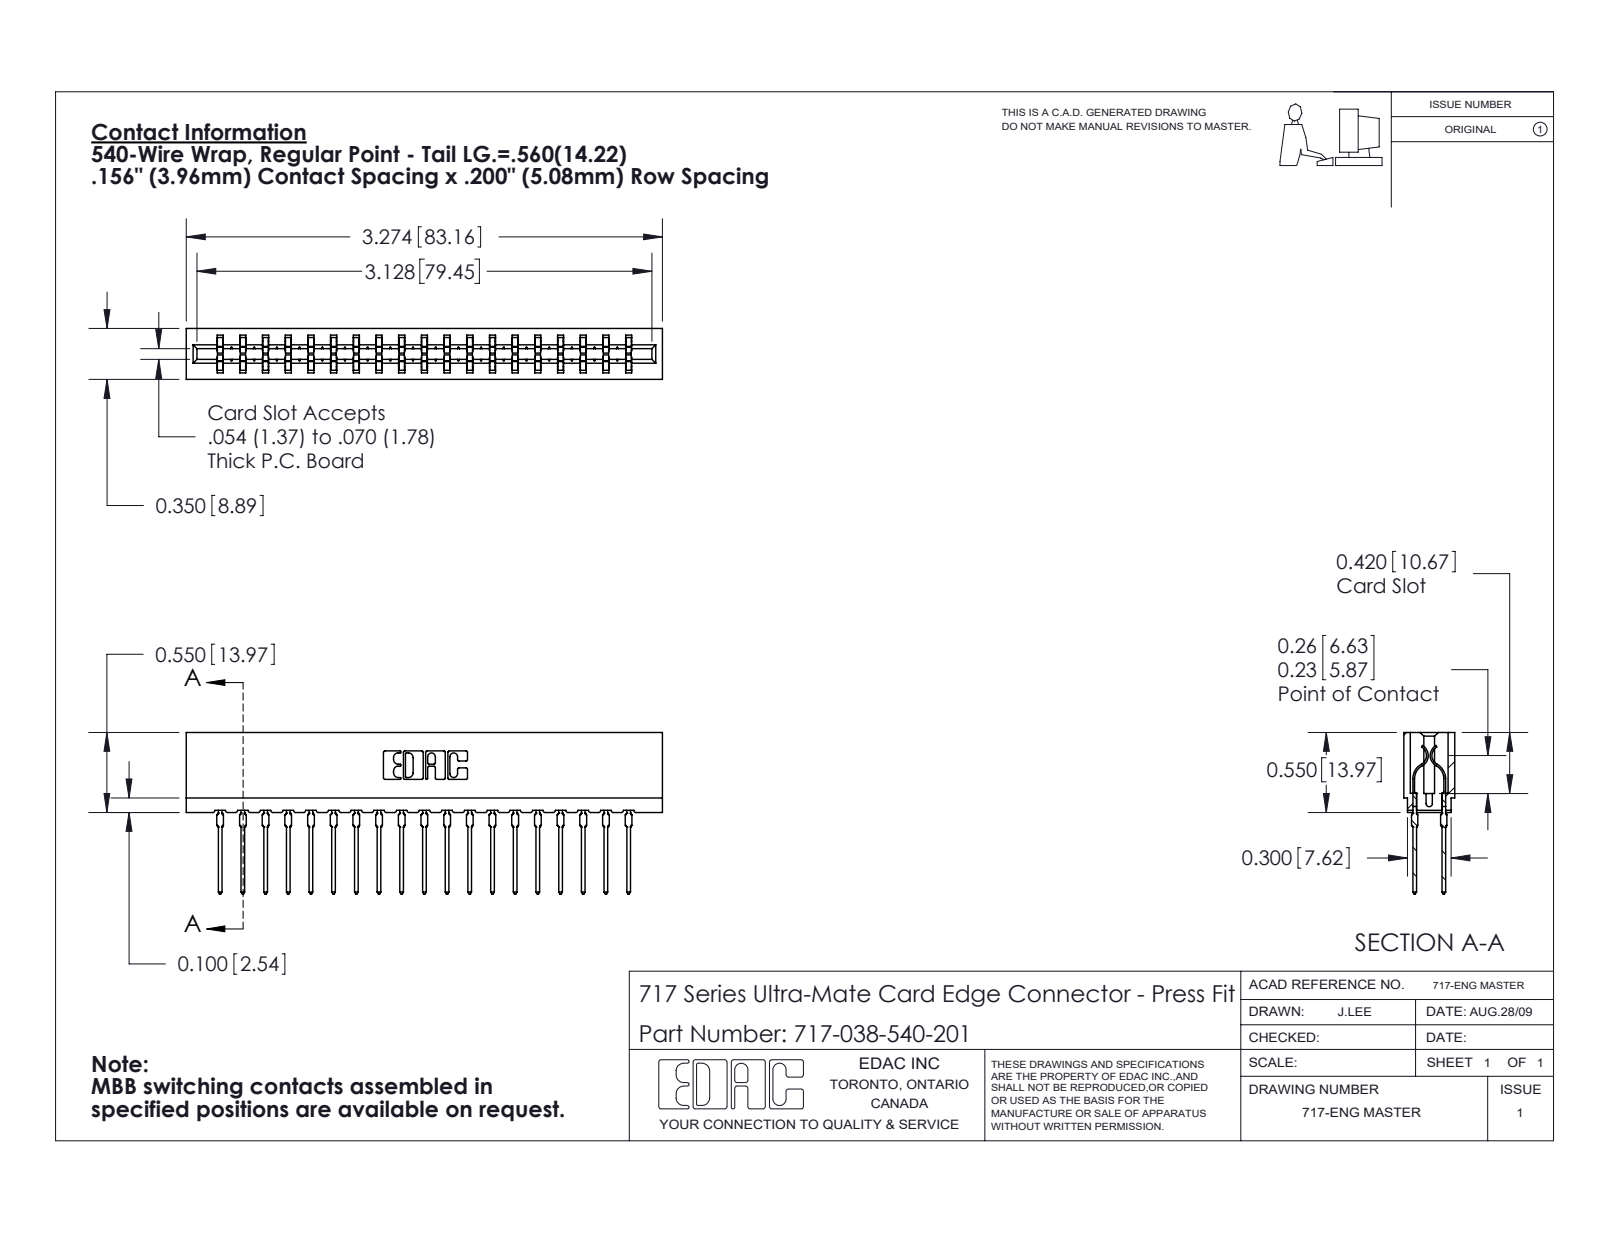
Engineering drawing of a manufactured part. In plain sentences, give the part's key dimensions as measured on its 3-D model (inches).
The part is named "717-038-540-201; 717 Part_Insulator Option - 06; 745-292-001_540". Its 3-D file was written by "SolidWorks 2020 (CONFIG_CONTROL_DESIGN)". It is 39 solids with 3514 faces: 1821 planar, 705 cylindrical and 988 other. Overall it measures 3.274 by 1.109 by 0.35 inches. Its volume is 0.452 cubic inches and its surface area 17.86 square inches. Partial cylindrical surfaces (rounded edges, fillets, slot ends): 76 of radius 0.021, 38 of radius 0.015, 22 of radius 0.01, 8 of radius 0.005, 8 of radius 0.011, 6 of radius 0.007, 6 of radius 0.031, 3 of radius 0.026. The main face-to-face distances are 0.212, 0.138, 0.35, 0.063, 0.287, 0.076, 0.149, 0.156, 0.624, 0.074.
